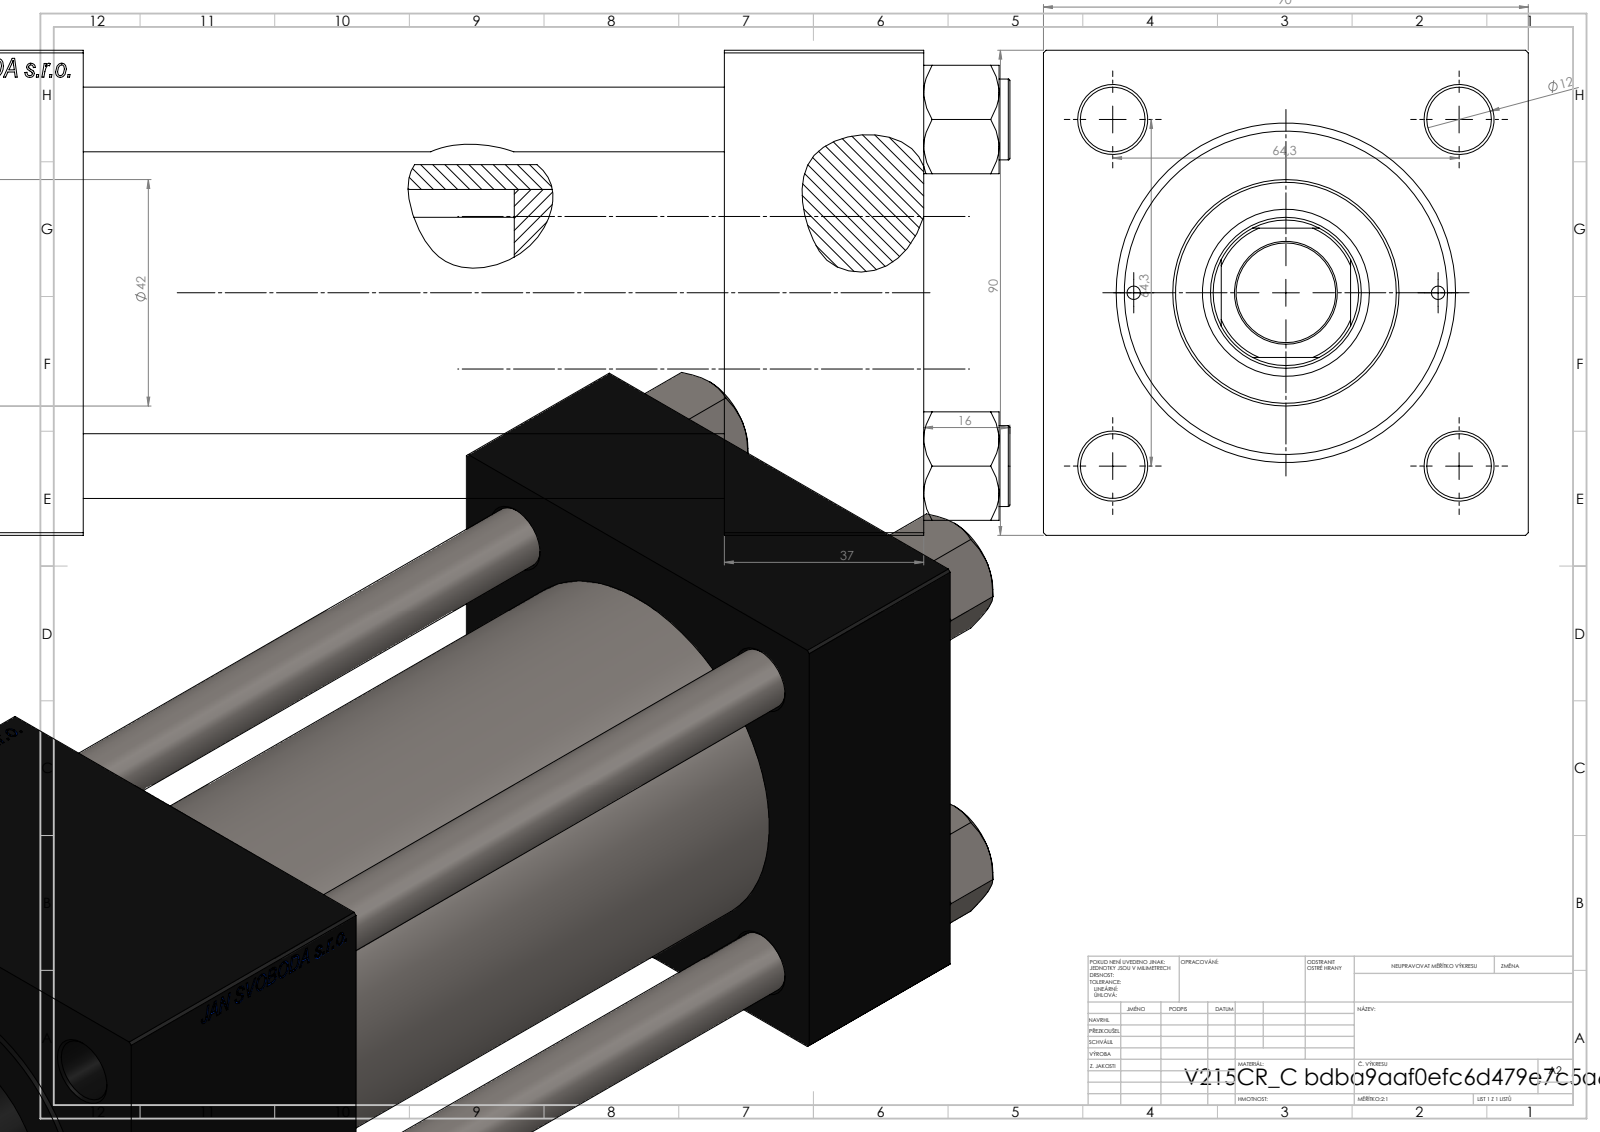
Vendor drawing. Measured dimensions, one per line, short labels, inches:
name: V215CR_VCP_C; V215_VC_A; V215CR_C_Body; NUT_M5_C (+1 more)
written by: SolidWorks 2019 (CONFIG_CONTROL_DESIGN)
unit: in
bodies: 11 solids, 1154 faces (528 planar, 90 cylindrical, 536 other)
size: 10.354 × 3.543 × 3.543
volume: 63.95 in³; area: 338.5 in²
holes: 4× ⌀0.472, 2× ⌀0.098, 2× ⌀0.276, 2× ⌀0.825, 2× ⌀1.181, 1× ⌀0.728, 1× ⌀1.102, 1× ⌀1.22, 1× ⌀1.969, 1× ⌀2.362, 1× ⌀2.48
bosses: 4× ⌀0.591, 1× ⌀2.717, 1× ⌀1.654
rounds: 1× R0.531
face distances: 3.543, 1.457, 8.465, 7.008, 6.142, 4.685, 2.323, 7.335, 5.878, 1.193
hole spacings: 1.275, 1.79, 2.531, 2.694, 1.112, 3.58, 2.224, 6.201
